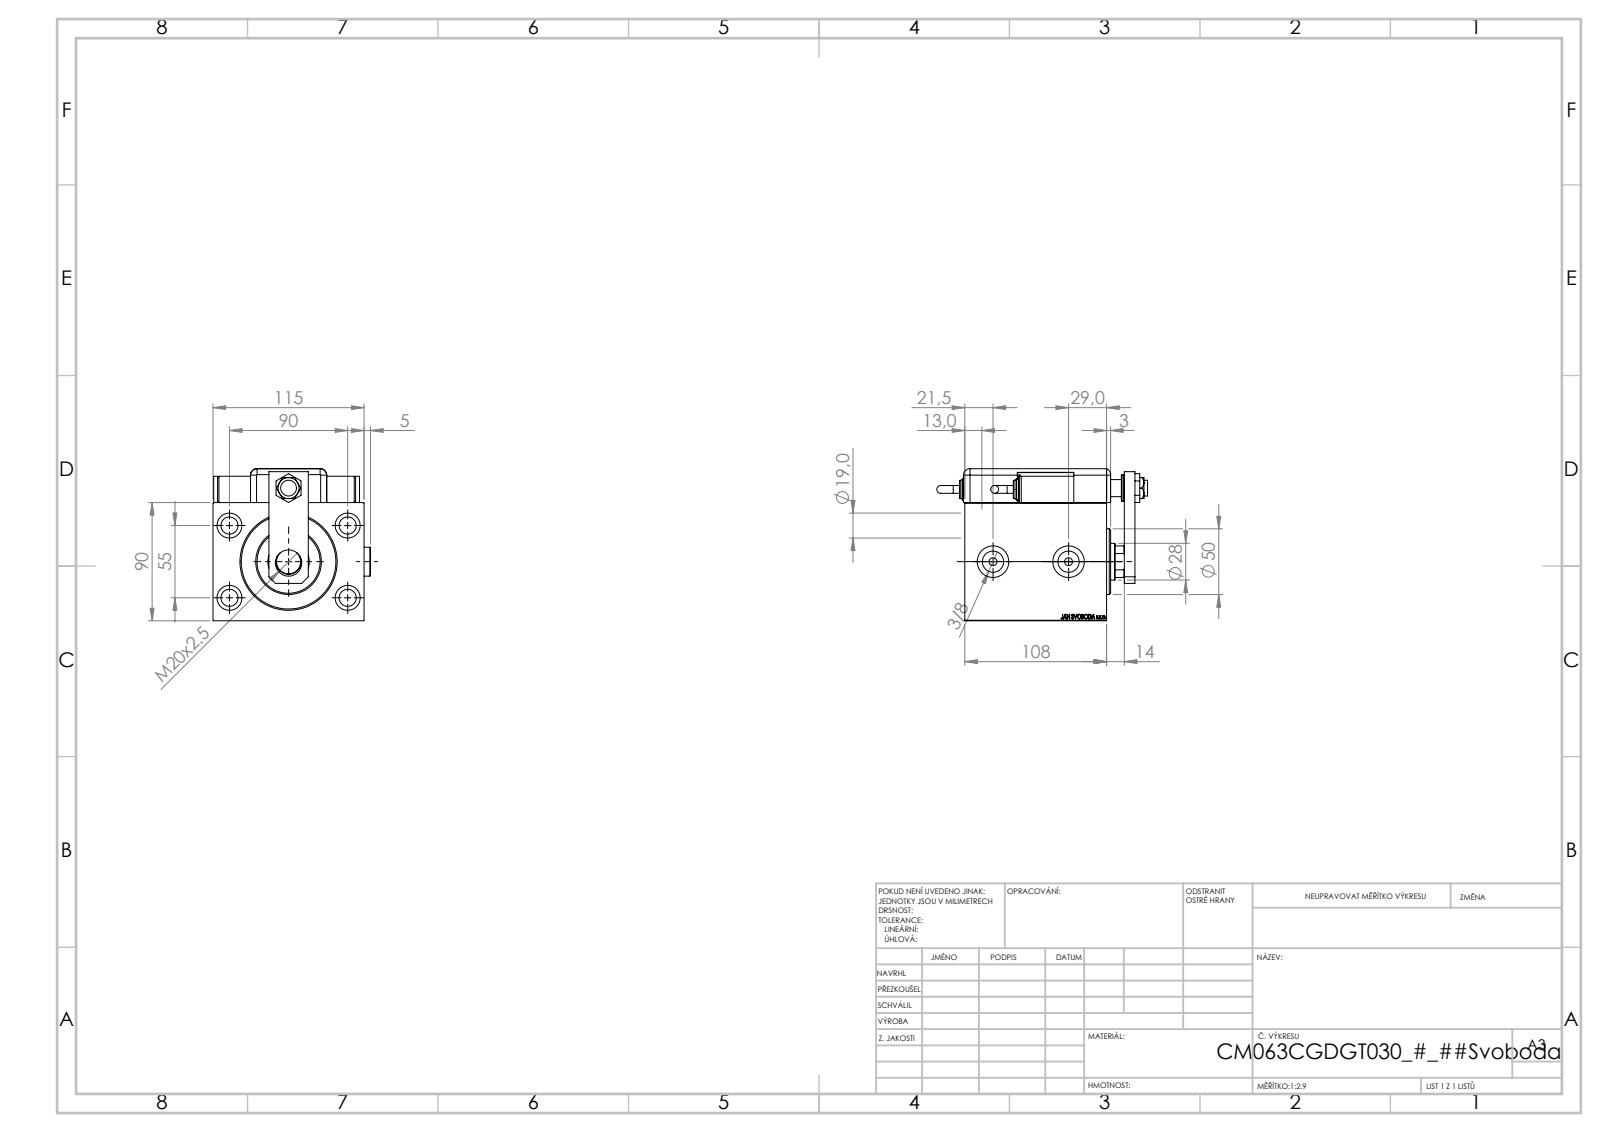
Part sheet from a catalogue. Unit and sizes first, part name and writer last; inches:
Units: inches
Overall size (bounding box): 6.317 × 4.72 × 4.559
Round holes (diameter × count): ⌀0.512 ×5, ⌀0.748 ×4, ⌀0.157 ×2, ⌀0.236 ×2, ⌀0.315 ×2, ⌀0.637 ×2, ⌀0.945 ×2, ⌀0.472 ×1, ⌀0.551 ×1, ⌀0.728 ×1, ⌀0.787 ×1, ⌀1.102 ×1
Round bosses / shafts (diameter × count): ⌀0.787 ×3, ⌀0.866 ×2, ⌀0.63 ×2, ⌀0.551 ×2, ⌀0.236 ×2, ⌀1.969 ×1
Partial cylindrical surfaces — rounded edges, fillets, slot ends (radius × count): R0.197 ×9, R0.394 ×1, R0.531 ×1
Main face-to-face distances: 3.543, 0.118, 4.252, 4.528, 3.563, 0.689, 0.531, 0.728, 0.315, 1.016
Hole centre spacings: 2.076, 2.097, 2.056, 2.165, 3.543, 3.734, 4.153, 0.039
Volume: 67.92 in³ · Surface area: 307.3 in²
Bodies: 15 solids, 1303 faces (649 planar, 133 cylindrical, 521 other)
Part name (STEP PRODUCT): MAGNETIC SWITCH Q; V450CM_C_VCP; ZARAZKA_Q; V450CM_C_Body (+7 more)
STEP written by: SolidWorks 2019 (CONFIG_CONTROL_DESIGN)
